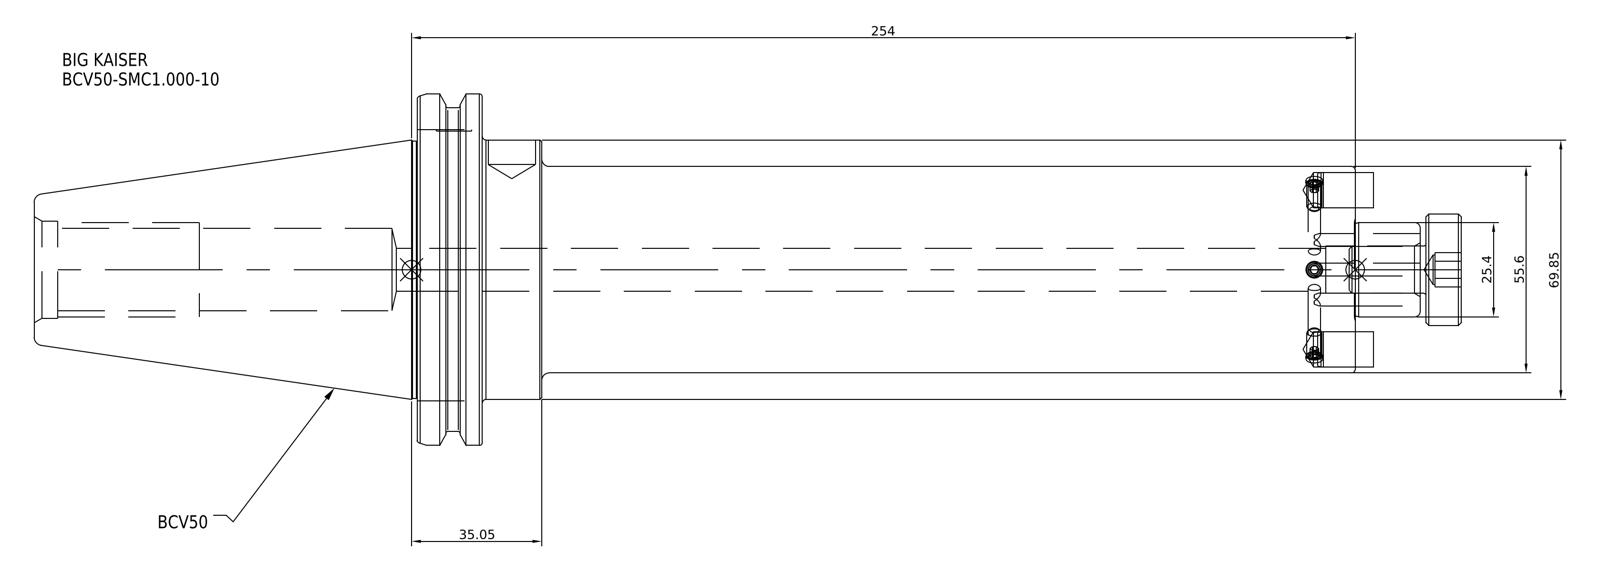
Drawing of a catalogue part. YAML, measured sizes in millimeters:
part_name: "BCV50-SMC1_000-10"
step_written_by: "SolidWorks 2021 (CONFIG_CONTROL_DESIGN)"
units: millimeters
bodies: {solids: 1, faces: 38, planar: 18, cylindrical: 14, other: 6}
overall_size: [360.5, 98.43, 98.43]
volume: 952379
surface_area: 87519
round_holes:
  - {diameter: 11.51, count: 1}
round_bosses_or_shafts:
  - {diameter: 98.43, count: 1}
  - {diameter: 91.29, count: 1}
  - {diameter: 69.85, count: 1}
  - {diameter: 55.6, count: 1}
face_to_face_distances: [17.55, 234.95, 252.5, 218.95, 16, 33.55, 355.6, 136.65, 120.65, 103.1]
